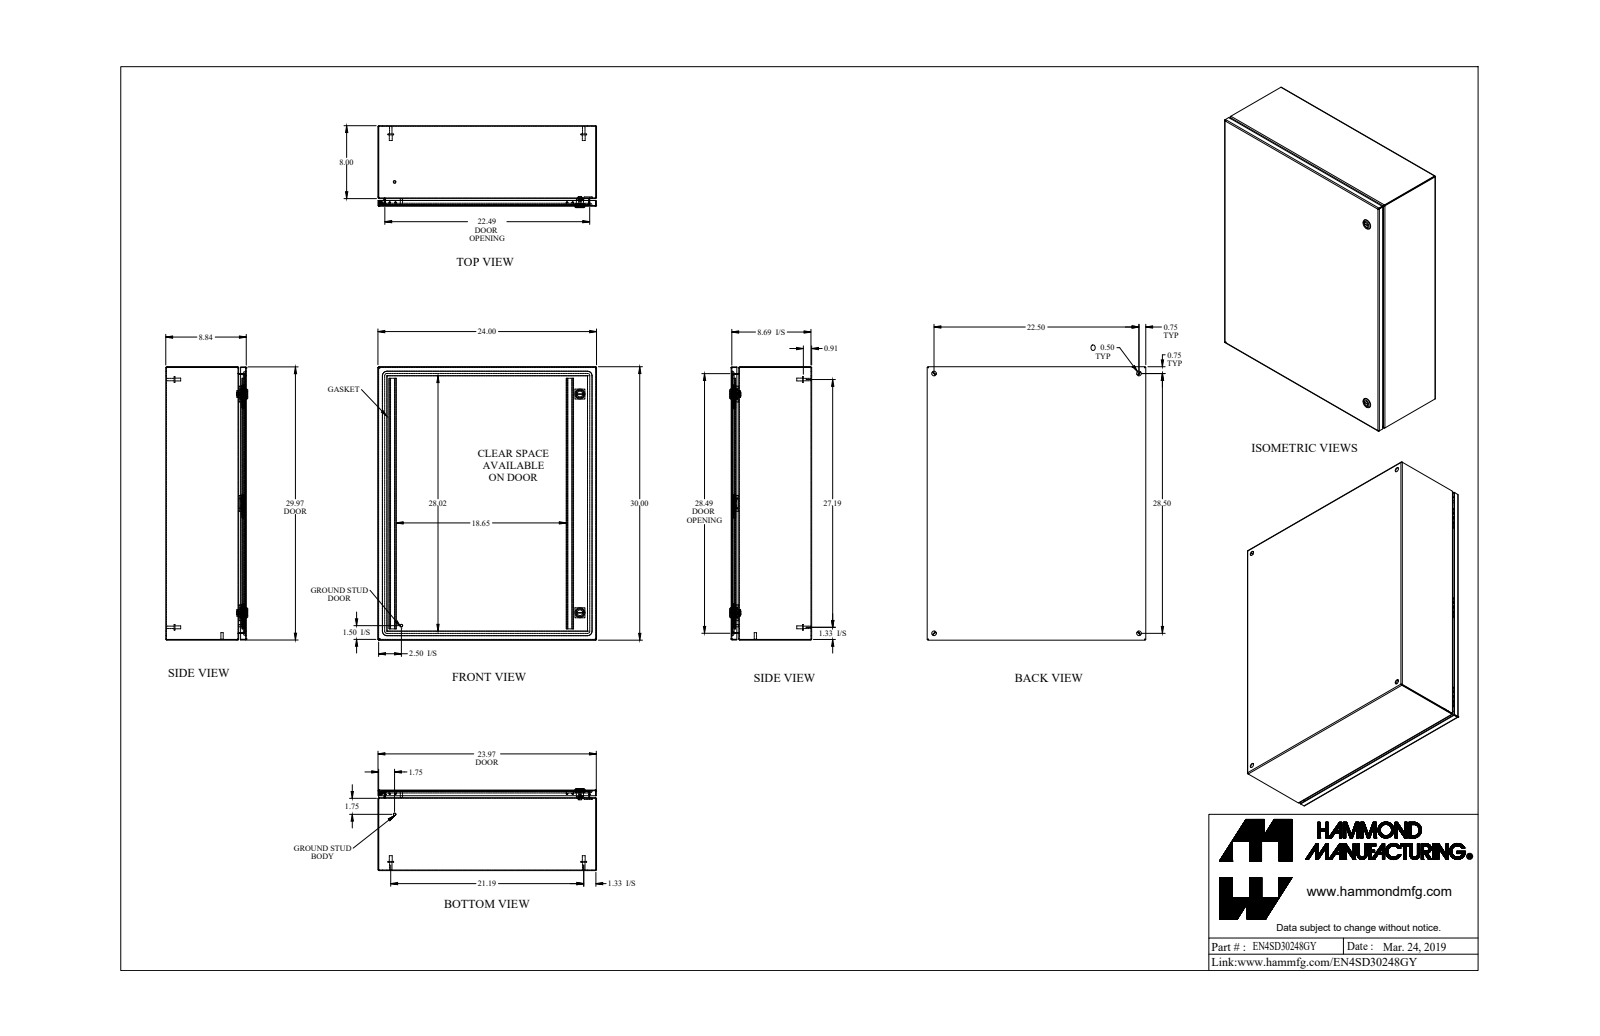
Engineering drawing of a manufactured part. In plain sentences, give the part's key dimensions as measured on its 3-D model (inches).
The part is named "EN4SD30248GY_Default". Its 3-D file was written by "SolidWorks 2019 (CONFIG_CONTROL_DESIGN)". It is 31 solids with 885 faces: 422 planar, 295 cylindrical and 168 other. Overall it measures 30 by 24 by 8.997 inches. Its volume is 195.4 cubic inches and its surface area 5 484 square inches. Round holes: 4 of diameter 0.5, 2 of diameter 0.232, 2 of diameter 0.625, 2 of diameter 0.785, 1 of diameter 0.172, 1 of diameter 0.24, 1 of diameter 0.242. Round bosses or shafts: 4 of diameter 0.625, 4 of diameter 0.313, 4 of diameter 0.27, 2 of diameter 1.1, 2 of diameter 0.525, 2 of diameter 0.281, 2 of diameter 0.25, 1 of diameter 0.455. Partial cylindrical surfaces (rounded edges, fillets, slot ends): 20 of radius 0.036, 20 of radius 0.108, 12 of radius 0.043, 12 of radius 0.081, 12 of radius 0.382, 8 of radius 19.003, 6 of radius 0.006, 6 of radius 0.062. The main face-to-face distances are 0.072, 8.765, 8.693, 8.837, 23.928, 29.928, 23.856, 24, 29.856, 30. The hole center spacings are 22.5, 28.5, 36.311, 2.493, 2.494, 21.545, 21.545, 23.999.
